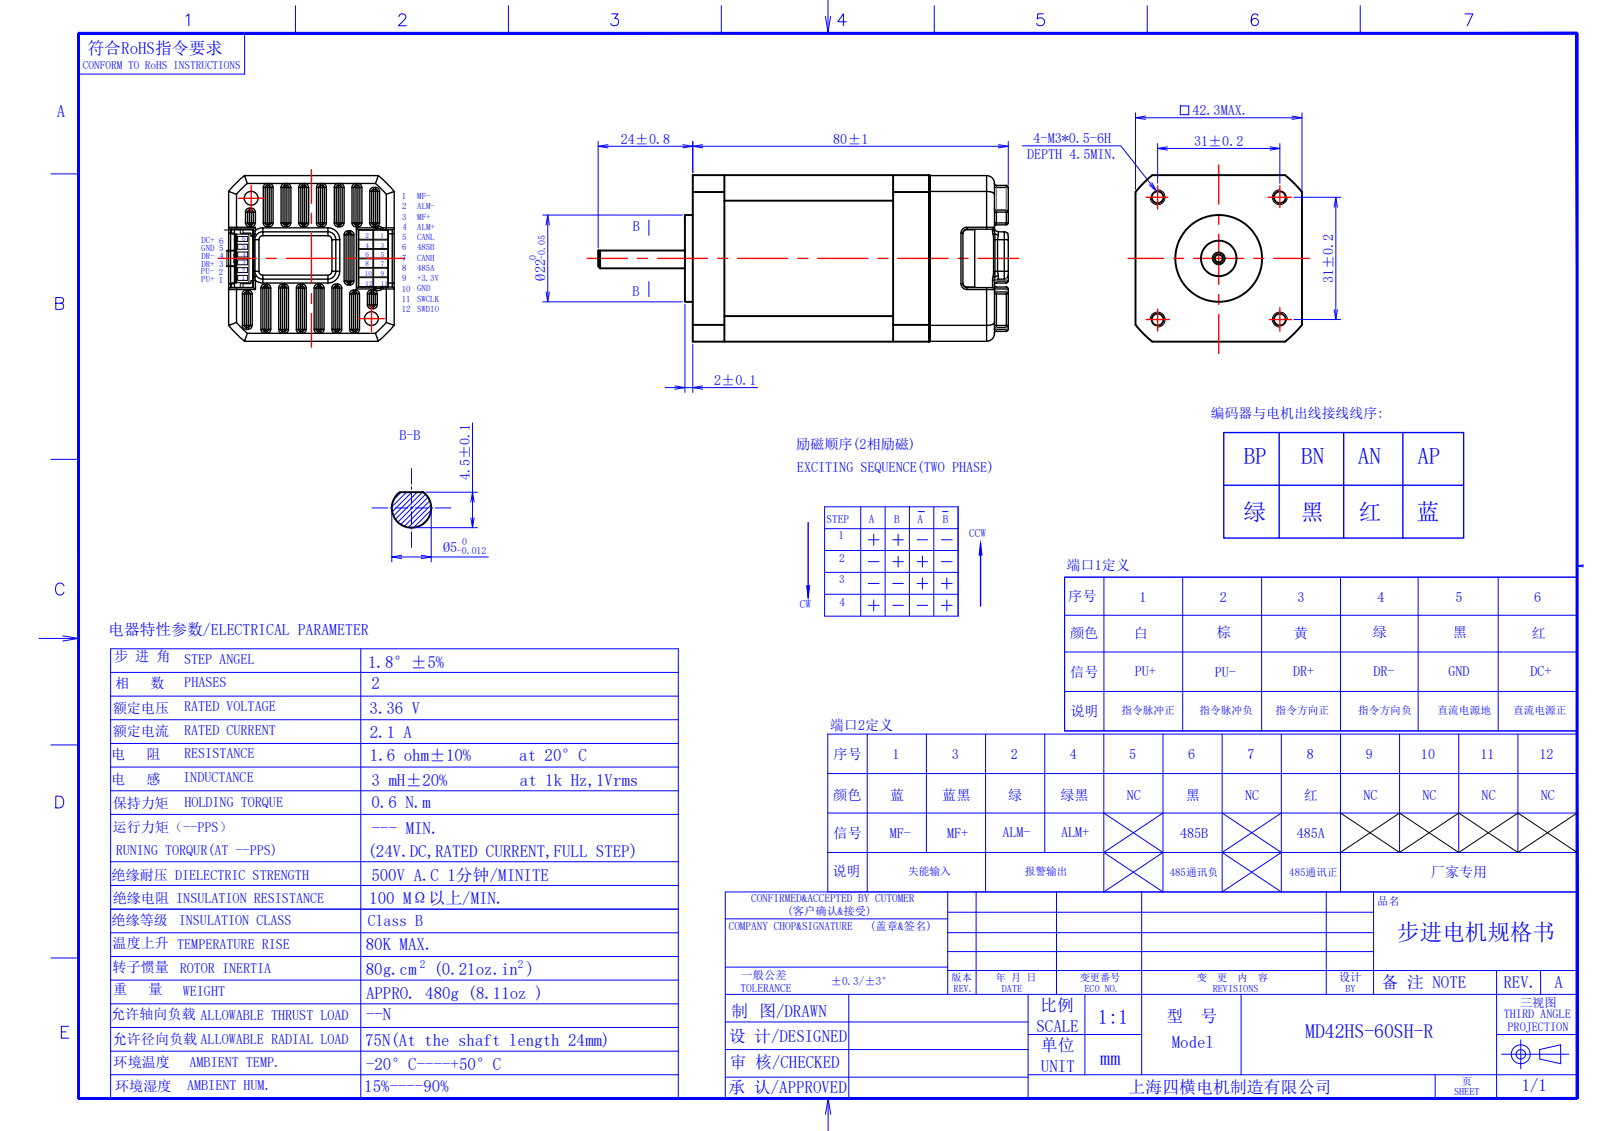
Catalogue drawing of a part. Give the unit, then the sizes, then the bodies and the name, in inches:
Units: inches
Overall size (bounding box): 4.094 × 1.665 × 1.665
Round holes (diameter × count): ⌀0.098 ×6, ⌀0.13 ×4, ⌀0.138 ×4, ⌀0.217 ×4, ⌀0.041 ×2, ⌀0.059 ×2, ⌀0.069 ×2, ⌀0.122 ×2, ⌀0.177 ×2, ⌀0.079 ×1, ⌀0.236 ×1, ⌀0.354 ×1
Round bosses / shafts (diameter × count): ⌀0.197 ×5, ⌀0.118 ×4, ⌀0.083 ×2, ⌀1.02 ×1, ⌀0.866 ×1, ⌀0.315 ×1
Partial cylindrical surfaces — rounded edges, fillets, slot ends (radius × count): R0.02 ×174, R0.059 ×37, R0.039 ×24, R0.016 ×8, R0.017 ×8, R0.079 ×8, R0.012 ×4, R0.033 ×2
Main face-to-face distances: 1.665, 2.362, 0.315, 1.693, 0.354, 0.059, 2.047, 1.659, 0.669, 2.008
Hole centre spacings: 1.211, 0.014, 0.056, 0.057, 0.674, 0.687, 0.706, 0.849
Volume: 6.718 in³ · Surface area: 67.02 in²
Bodies: 13 solids, 1758 faces (932 planar, 545 cylindrical, 281 other)
Part name (STEP PRODUCT): 螺纹圈; MD42HS-60SH-R; M3螺钉-L73mm; 42H260-L87mm (+8 more)
STEP written by: SolidWorks 2022 (CONFIG_CONTROL_DESIGN)
